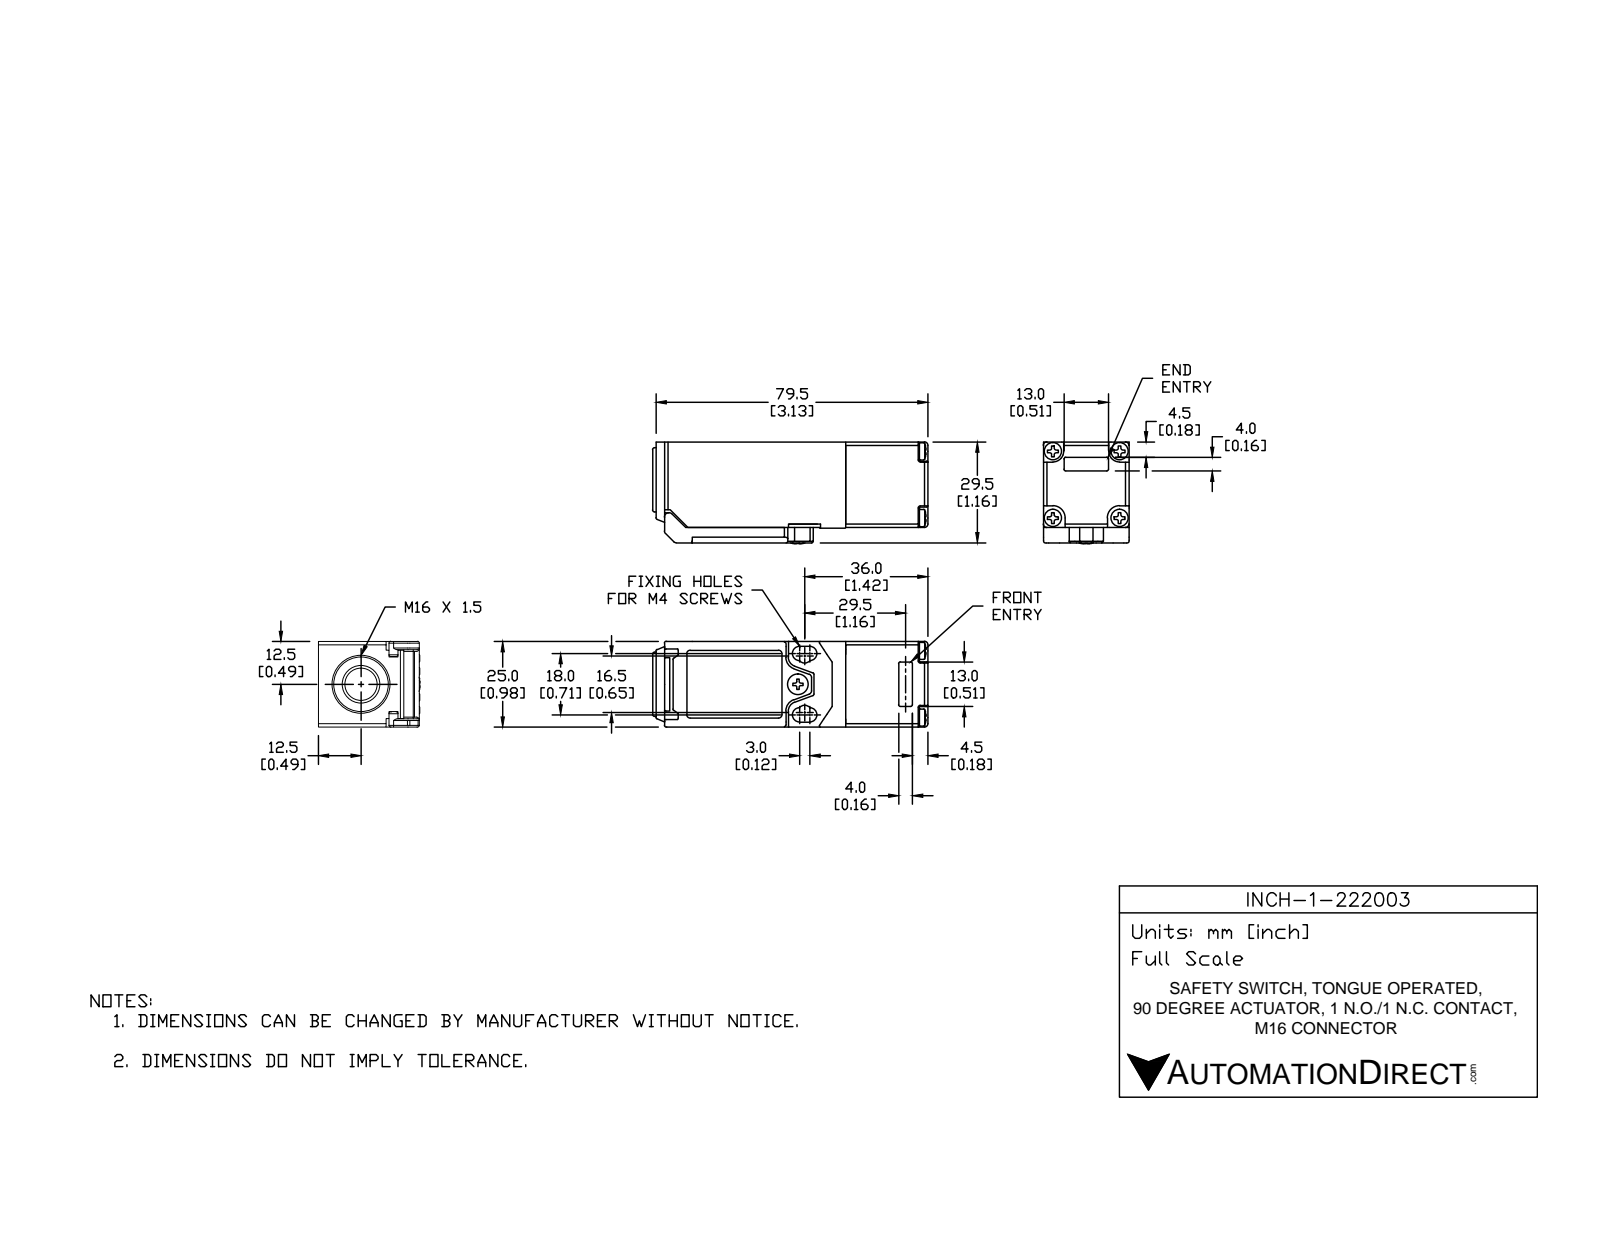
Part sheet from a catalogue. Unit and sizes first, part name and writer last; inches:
Units: inches
Overall size (bounding box): 3.169 × 1.172 × 0.984
Round holes (diameter × count): ⌀0.126 ×5, ⌀0.094 ×4, ⌀0.059 ×2, ⌀0.063 ×2, ⌀0.071 ×2, ⌀0.087 ×2, ⌀0.142 ×2, ⌀0.055 ×1, ⌀0.098 ×1, ⌀0.102 ×1, ⌀0.197 ×1, ⌀0.217 ×1
Round bosses / shafts (diameter × count): ⌀0.102 ×5, ⌀0.197 ×4, ⌀0.079 ×4, ⌀0.138 ×2, ⌀0.74 ×1, ⌀0.531 ×1, ⌀0.213 ×1, ⌀0.118 ×1
Partial cylindrical surfaces — rounded edges, fillets, slot ends (radius × count): R0.02 ×236, R0.012 ×85, R0.004 ×24, R0.039 ×24, R0.031 ×10, R0.083 ×6, R0.11 ×6, R0.008 ×4
Main face-to-face distances: 0.984, 0.079, 0.039, 0.906, 0.02, 0.874, 0.024, 0.945, 0.929, 0.913
Hole centre spacings: 0.543, 0.768, 0.171, 0.187, 0.423, 0.426, 0.45, 0.581
Volume: 1.453 in³ · Surface area: 40.72 in²
Bodies: 14 solids, 1863 faces (738 planar, 677 cylindrical, 448 other)
Part name (STEP PRODUCT): INCH-1-222003
STEP written by: SolidWorks 2014 (AUTOMOTIVE_DESIGN)
